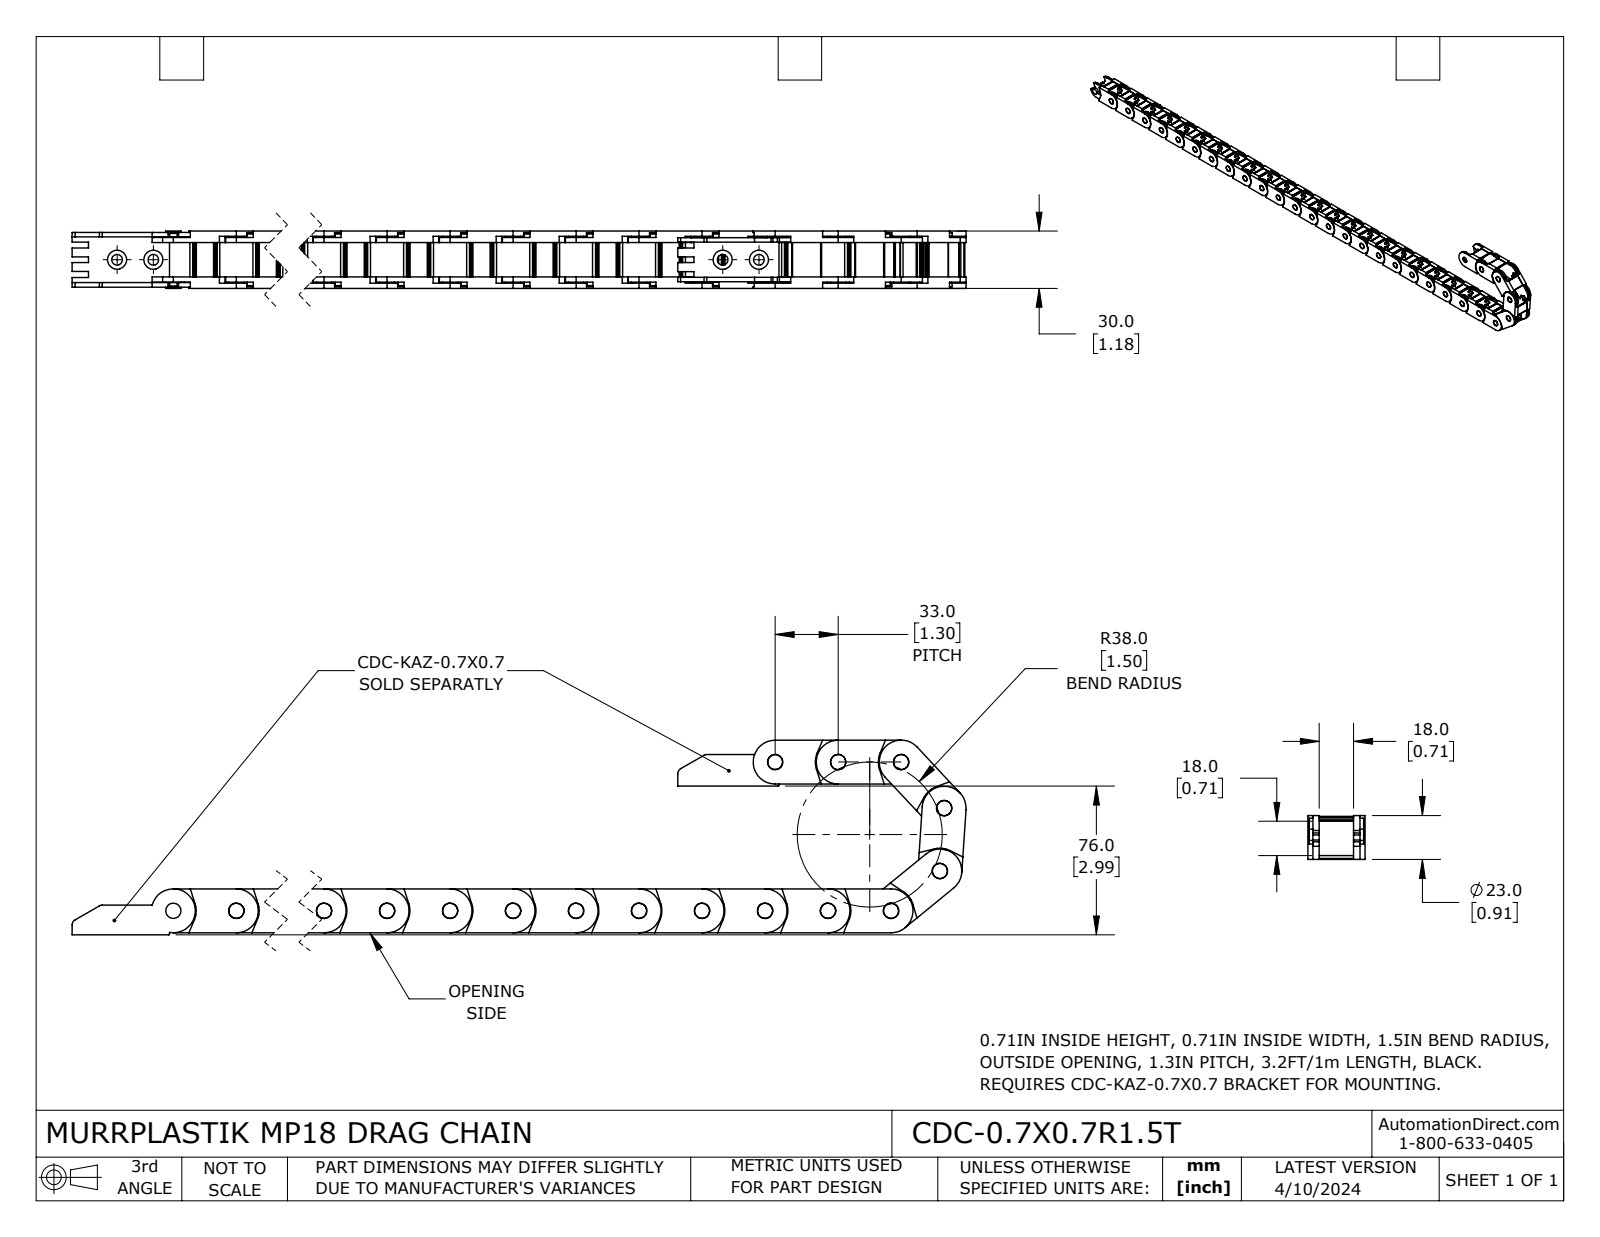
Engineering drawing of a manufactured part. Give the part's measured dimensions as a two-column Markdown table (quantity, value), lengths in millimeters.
| quantity | value |
| --- | --- |
| part name | CDC-0.7X0.7R1.5T |
| STEP written by | SolidWorks 2023 (CONFIG_CONTROL_DESIGN) |
| units | millimeters |
| bodies | 29 solids, 2639 faces (1479 planar, 1160 cylindrical, 0 other) |
| overall size | 842.49 × 100.88 × 30 |
| volume | 255 262 mm³ |
| surface area | 200 586 mm² |
| round holes (diameter × count) | 8 × 29 |
| round bosses / shafts (diameter × count) | 8 × 1 |
| partial cylindrical surfaces (radius × count) | 0.5 × 116, 1.5 × 116, 0.2 × 58, 0.3 × 58, 11.5 × 30, 11.95 × 30, 5 × 29, 5.45 × 29 |
| main face-to-face distances | 24, 6, 2.7, 3.3, 30, 26.7, 20.7, 18, 27.3, 0.6 |
| hole center spacings | 33, 66, 99, 132, 165, 198, 231, 264 |
